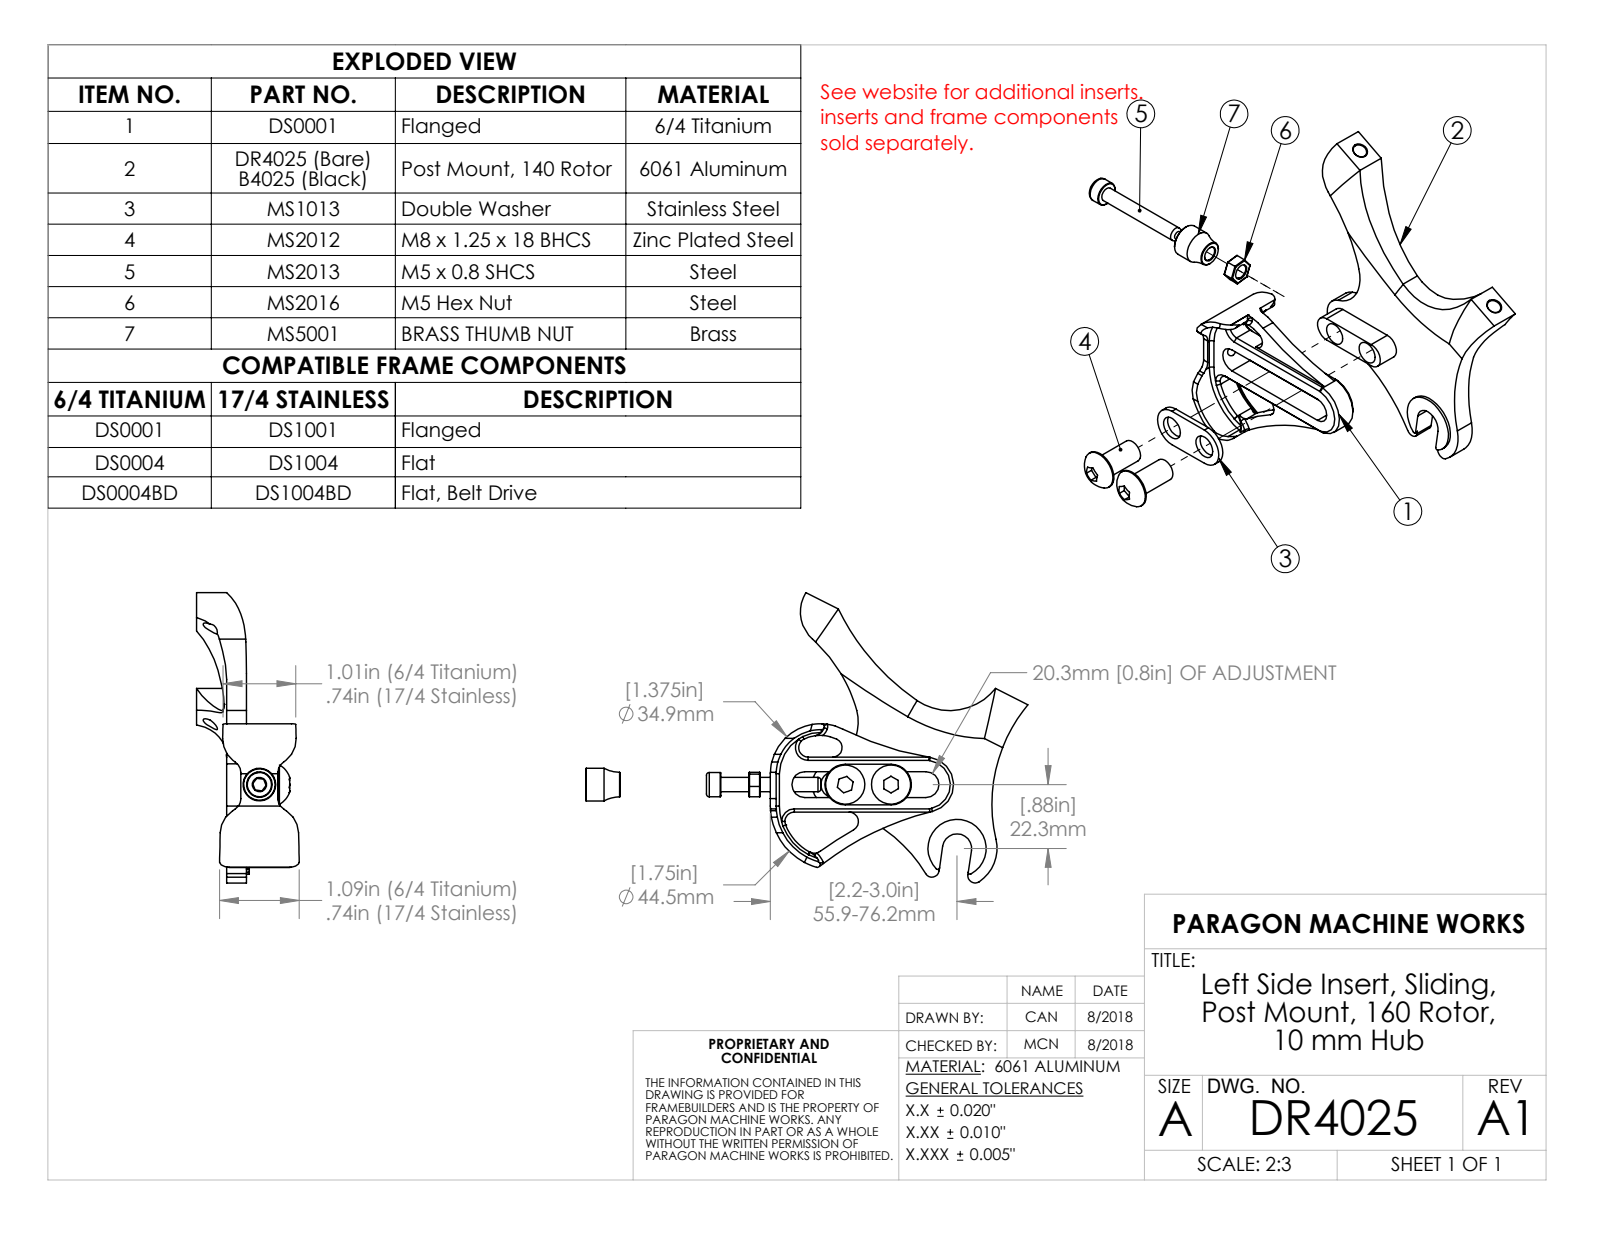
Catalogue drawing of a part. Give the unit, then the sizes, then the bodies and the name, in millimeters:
Units: millimetres
Overall size (bounding box): 101.3 × 80.1 × 25.4
Round holes (diameter × count): ⌀5 ×2, ⌀7.9 ×2
Round bosses / shafts (diameter × count): ⌀20.3 ×1
Partial cylindrical surfaces — rounded edges, fillets, slot ends (radius × count): R0.6 ×2, R2.5 ×2, R4.5 ×2, R6.4 ×2, R15.2 ×2, R25.4 ×2, R50.8 ×2, R5.1 ×1
Main face-to-face distances: 7, 10.5, 17.4, 18.4, 7.9, 1, 9, 25.4, 14.9, 8
Hole centre spacings: 16, 74.3
Volume: 26 470 mm³ · Surface area: 11 290 mm²
Bodies: 1 solid, 55 faces (15 planar, 36 cylindrical, 4 other)
Part name (STEP PRODUCT): DR4025MOD
STEP written by: SolidWorks 2023 (AUTOMOTIVE_DESIGN)
